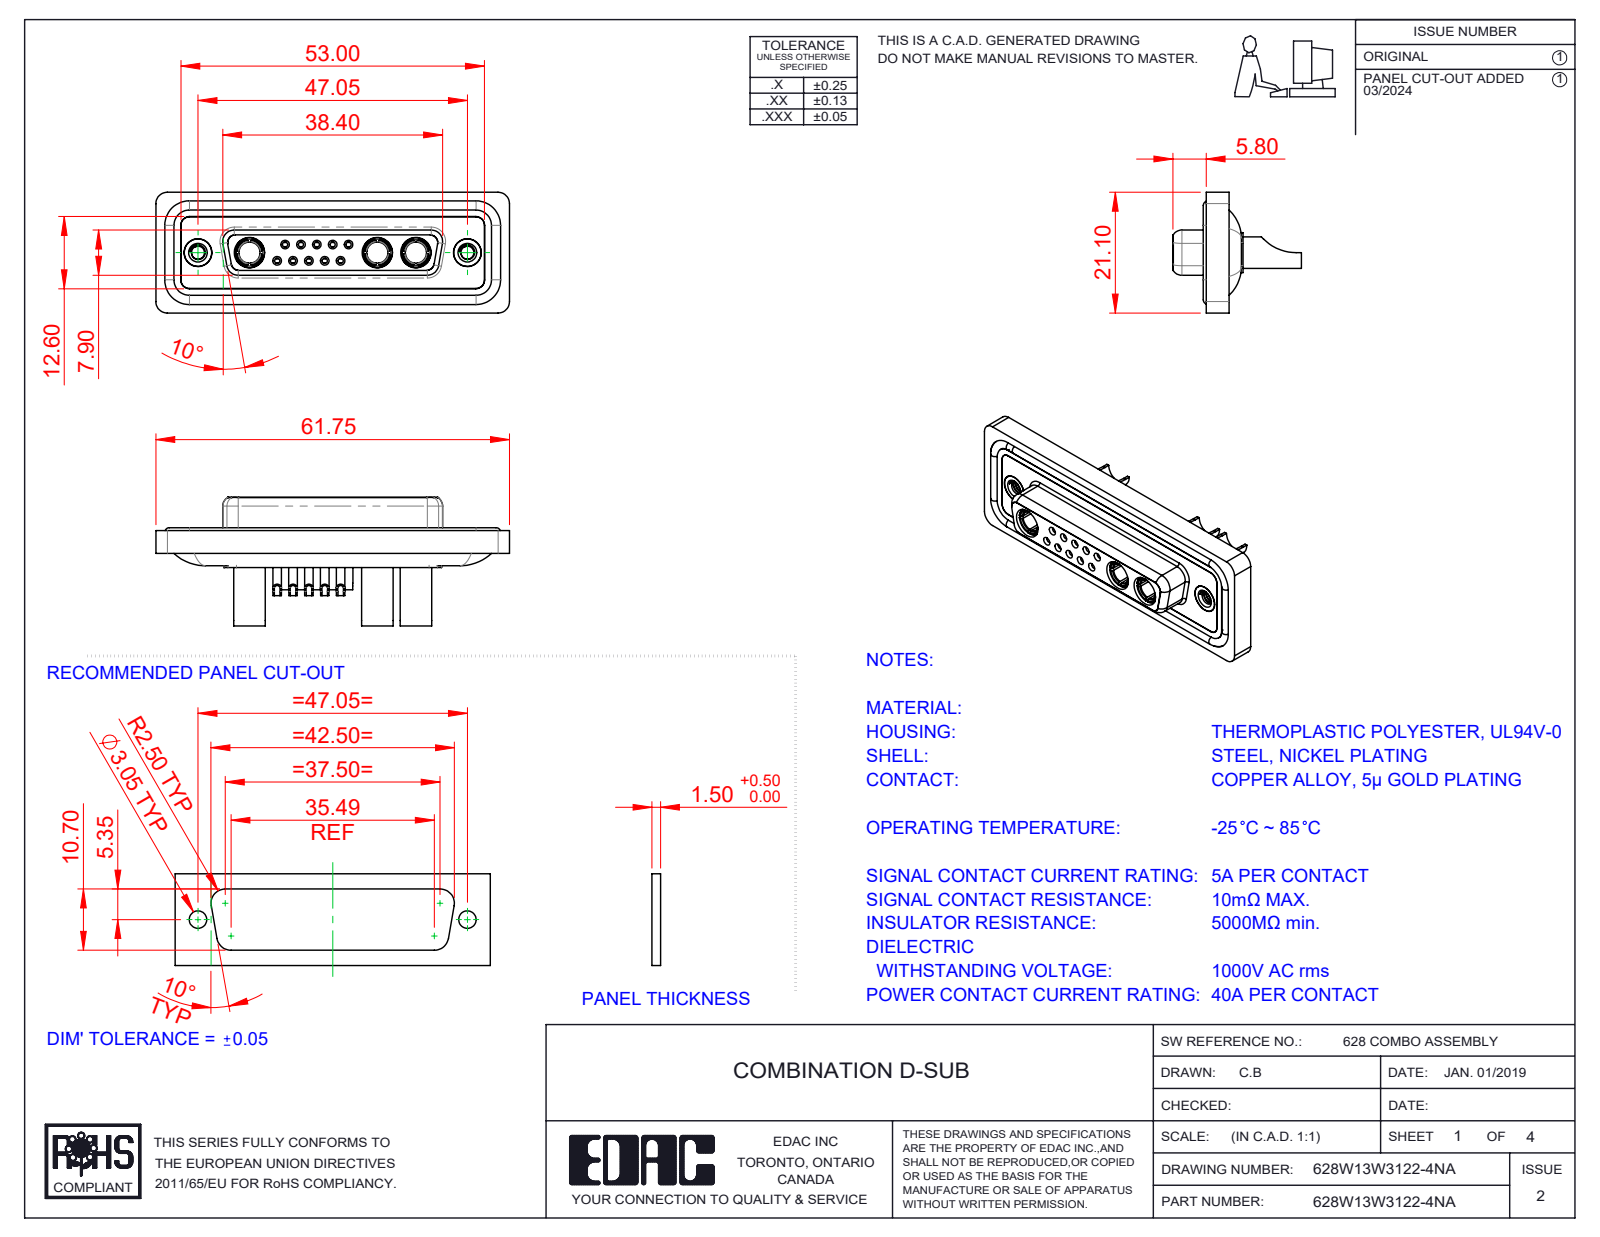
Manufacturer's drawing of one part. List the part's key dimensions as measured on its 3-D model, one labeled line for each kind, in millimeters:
Part name (STEP PRODUCT): 628Combo Shell Front_25 Contacts; 628Combo Housing_13W3; Power Socket_40A SC; 628Combo Waterproof Housing_25 Contacts (+5 more)
STEP written by: SolidWorks 2023 (CONFIG_CONTROL_DESIGN)
Units: millimetres
Bodies: 23 solids, 1165 faces (368 planar, 472 cylindrical, 325 other)
Overall size (bounding box): 61.75 × 22.45 × 21.1
Volume: 8 415 mm³ · Surface area: 14 231 mm²
Round holes (diameter × count): ⌀0.9 ×10, ⌀1 ×10, ⌀1.1 ×10, ⌀1.5 ×10, ⌀2 ×10, ⌀1.6 ×5, ⌀1.7 ×5, ⌀4.85 ×5, ⌀3.7 ×3, ⌀4.6 ×3, ⌀5.3 ×3, ⌀2.26 ×2
Round bosses / shafts (diameter × count): ⌀2.2 ×10, ⌀1.6 ×9, ⌀5.5 ×3, ⌀5.2 ×3, ⌀4.96 ×3, ⌀4.75 ×3, ⌀3.75 ×3, ⌀4.95 ×2
Partial cylindrical surfaces — rounded edges, fillets, slot ends (radius × count): R1.5 ×22, R2 ×18, R1.35 ×8, R1.6 ×8, R1 ×6, R0.25 ×4, R0.5 ×4, R0.6 ×4
Main face-to-face distances: 0.4, 7.45, 1.8, 5.65, 0.5, 6.6, 7.05, 1.6, 2.9, 1.1
Hole centre spacings: 3.16, 2.77, 5.03, 5.04, 5.54, 8.31, 7.49, 2.76
